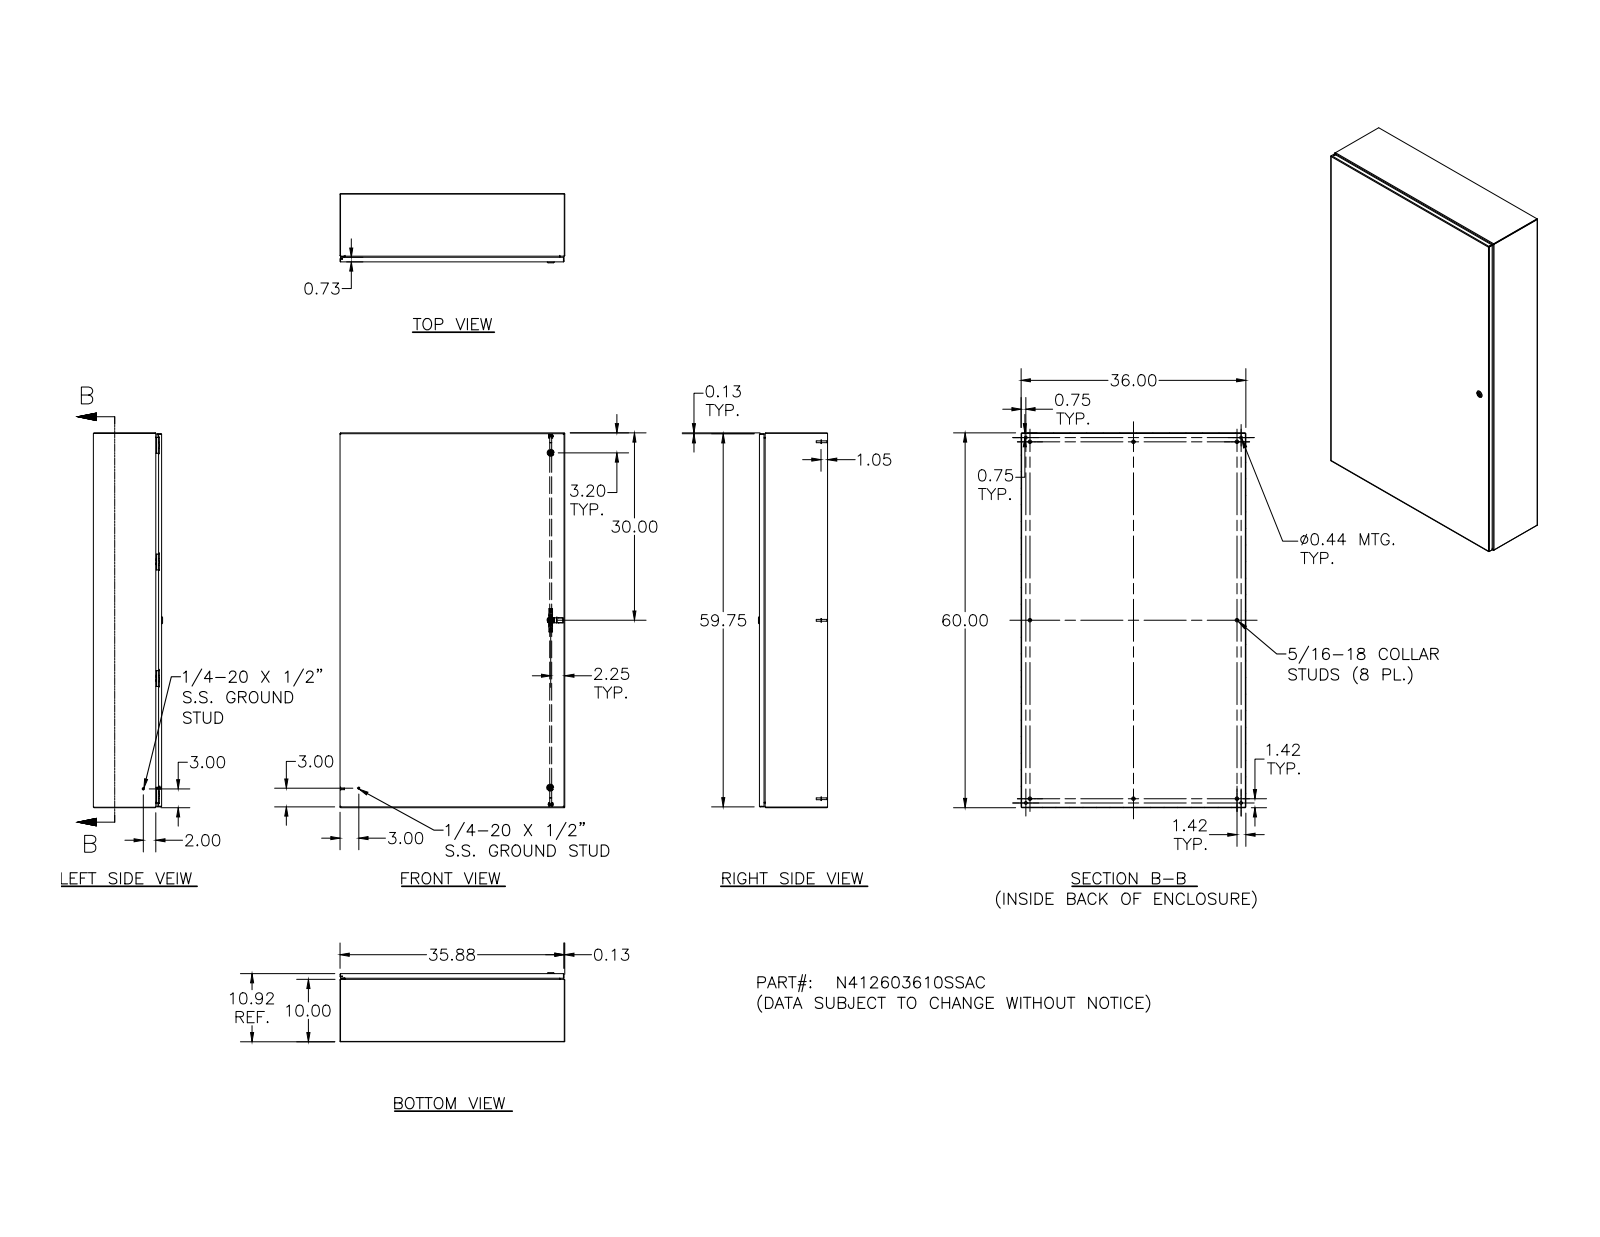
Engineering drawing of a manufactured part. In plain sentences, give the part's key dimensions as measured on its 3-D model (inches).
The part is named "N412603610SSAC; N412603610SSACBLR; N4123610SSACTB; 388151 (+8 more)". Its 3-D file was written by "Autodesk Inventor 2011 (AUTOMOTIVE_DESIGN)". It is 81 solids with 2661 faces: 988 planar, 992 cylindrical and 681 other. Overall it measures 60 by 36 by 11.075 inches. Its volume is 496 cubic inches and its surface area 13 378 square inches. Round holes: 8 of diameter 0.093, 8 of diameter 0.152, 8 of diameter 0.167, 8 of diameter 0.172, 8 of diameter 0.187, 5 of diameter 0.197, 4 of diameter 0.156, 4 of diameter 0.165, 4 of diameter 0.438, 2 of diameter 0.106, 2 of diameter 0.16, 2 of diameter 0.169. Round bosses or shafts: 18 of diameter 0.25, 8 of diameter 0.563, 8 of diameter 0.36, 8 of diameter 0.32, 8 of diameter 0.3, 8 of diameter 0.275, 8 of diameter 0.256, 8 of diameter 0.164. Partial cylindrical surfaces (rounded edges, fillets, slot ends): 50 of radius 0.05, 36 of radius 0.031, 34 of radius 0.016, 32 of radius 0.125, 30 of radius 0.012, 20 of radius 0.02, 18 of radius 0.105, 18 of radius 0.118. The main face-to-face distances are 0.074, 10.843, 10.769, 10.917, 35.926, 59.926, 35.852, 36, 59.852, 60. The hole center spacings are 18.667, 37.333, 18.667, 56, 0.5, 0.656, 1.307, 18.673.
